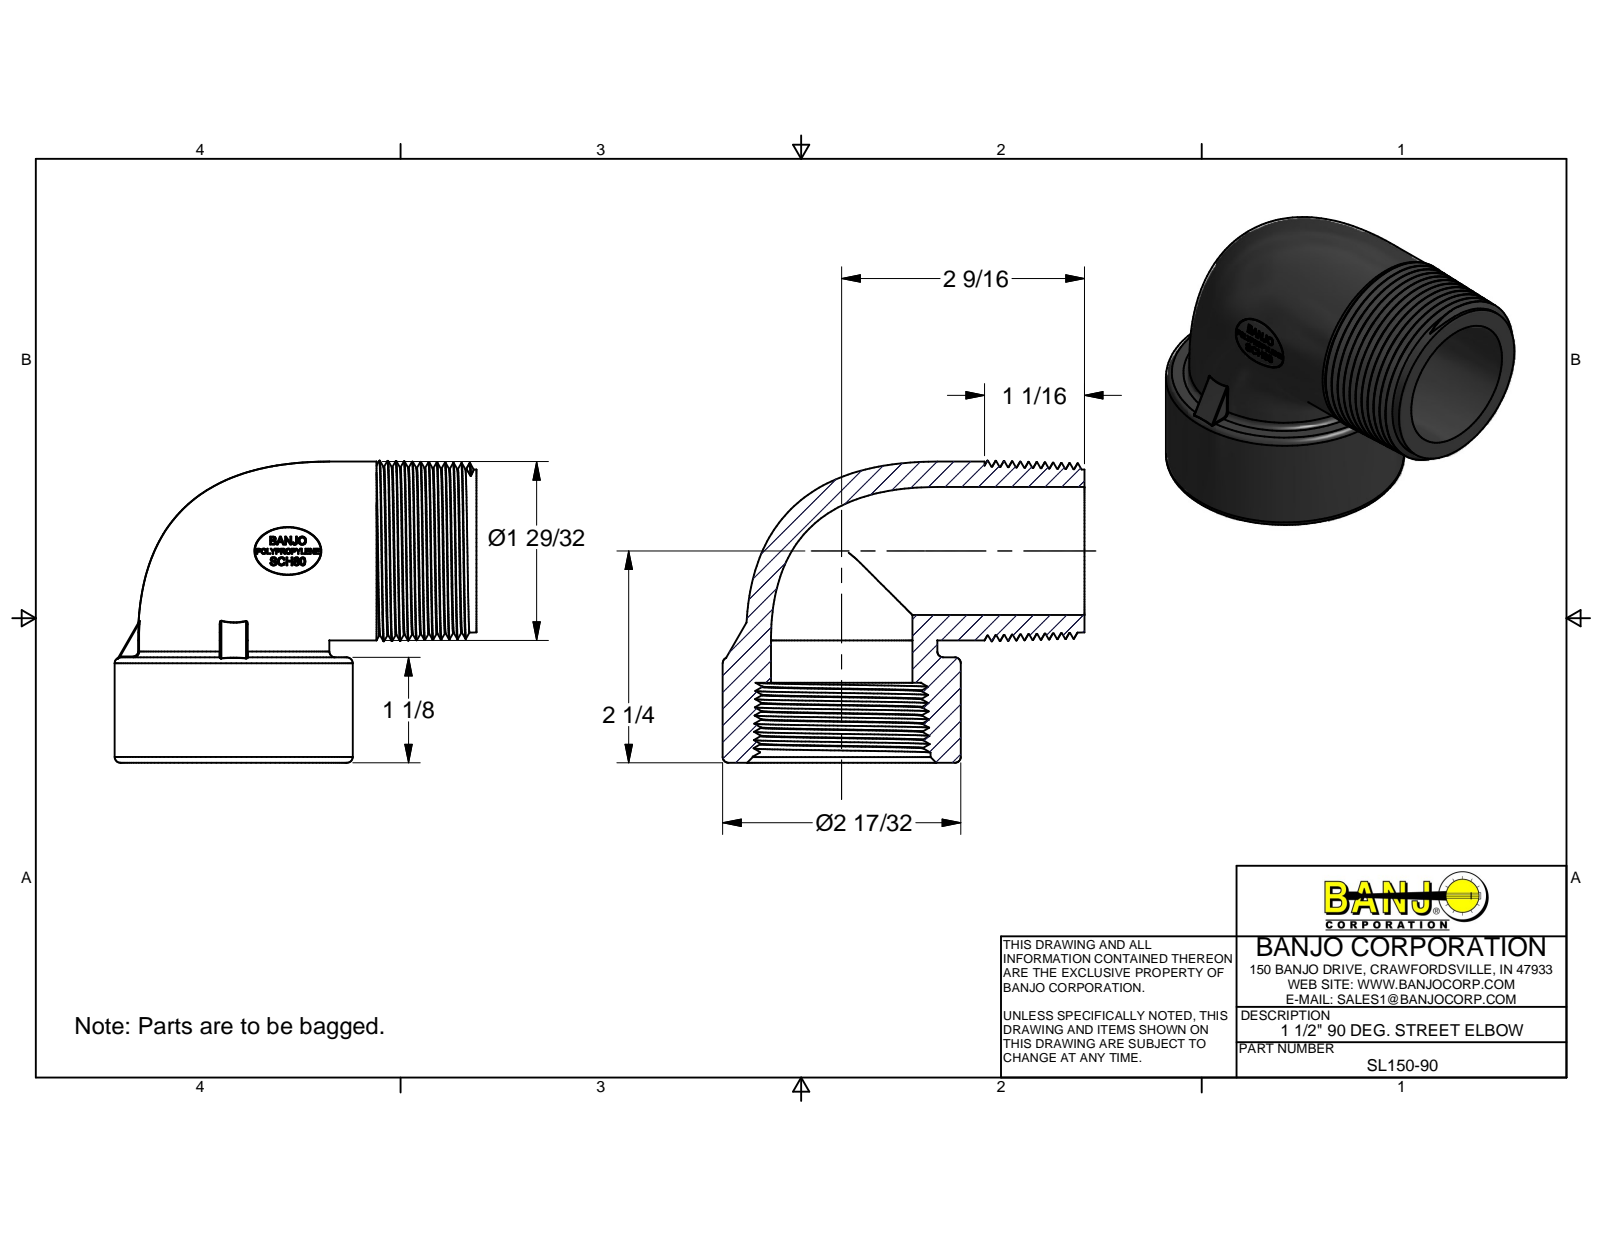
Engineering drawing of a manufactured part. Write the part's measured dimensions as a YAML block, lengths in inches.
part_name: "SL150-90"
step_written_by: "Mechanical Desktop 2009 (CONFIG_CONTROL_DESIGN)"
units: inches
bodies: {solids: 1, faces: 121, planar: 15, cylindrical: 10, other: 96}
overall_size: [3.838, 3.2, 2.526]
volume: 7.55
surface_area: 67.14
round_holes:
  - {diameter: 1.36, count: 1}
round_bosses_or_shafts:
  - {diameter: 1.9, count: 2}
  - {diameter: 2.526, count: 1}
  - {diameter: 1.73, count: 1}
face_to_face_distances: [1.12, 0.87, 0.25, 1.06, 0.956, 0.104, 1.378, 2.334, 2.437, 0.275]
